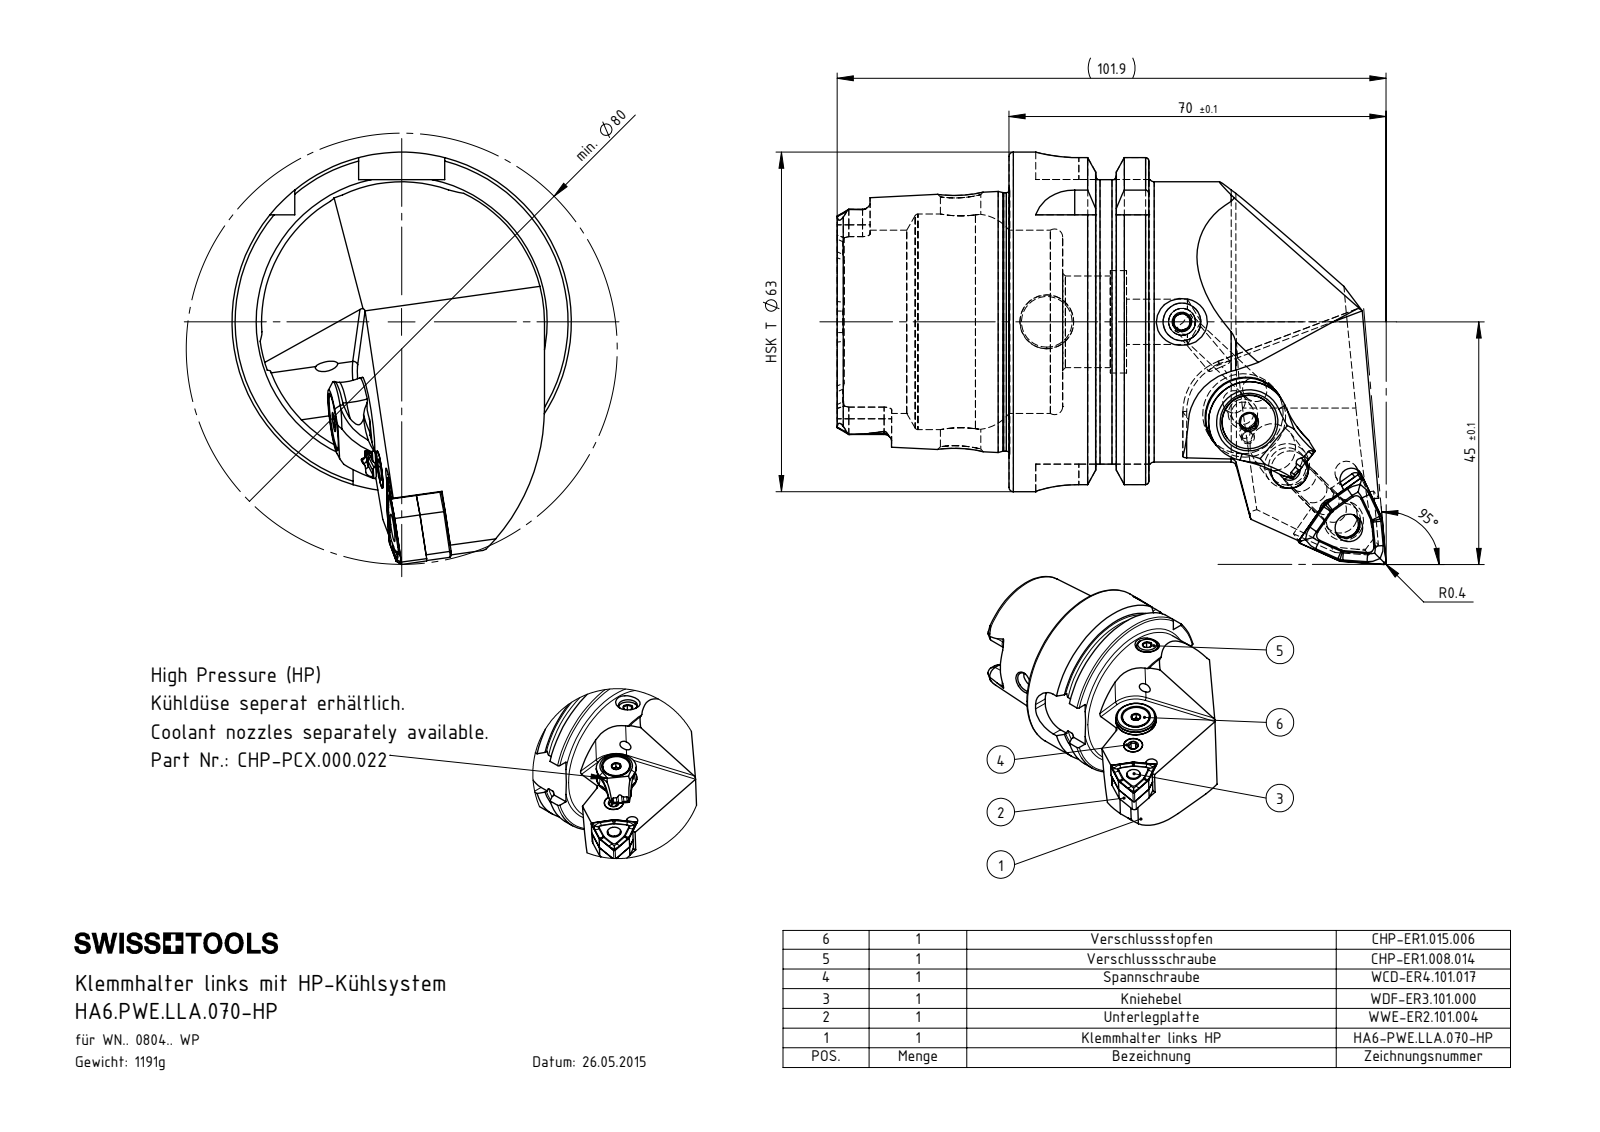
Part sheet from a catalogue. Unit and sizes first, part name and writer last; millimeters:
Units: millimetres
Overall size (bounding box): 49 × 47.34 × 41.9
Round holes (diameter × count): ⌀1.2 ×1, ⌀2.5 ×1, ⌀3 ×1, ⌀5.16 ×1, ⌀5.2 ×1, ⌀6.7 ×1, ⌀7.8 ×1
Round bosses / shafts (diameter × count): ⌀8 ×2, ⌀15 ×1, ⌀13.4 ×1, ⌀10 ×1, ⌀7.9 ×1, ⌀6.4 ×1, ⌀5.5 ×1, ⌀5 ×1
Partial cylindrical surfaces — rounded edges, fillets, slot ends (radius × count): R0.4 ×3, R1 ×3, R2.35 ×1, R2.8 ×1, R3.1 ×1, R3.2 ×1
Main face-to-face distances: 4.75, 4.76, 4.72, 5.8, 10.52, 10.55, 10.56, 4.7, 6.47, 16.92
Hole centre spacings: 24.74, 24.75, 4.47, 4.49, 28.5, 28.51
Volume: 4 102 mm³ · Surface area: 4 428 mm²
Bodies: 10 solids, 269 faces (102 planar, 56 cylindrical, 111 other)
Part name (STEP PRODUCT): PW..LLA.070-HP; WNMG080404; CHP-ER1.015.006_A; WDF-ER3.101.000_A (+8 more)
STEP written by: SolidWorks 2017 (AUTOMOTIVE_DESIGN)
